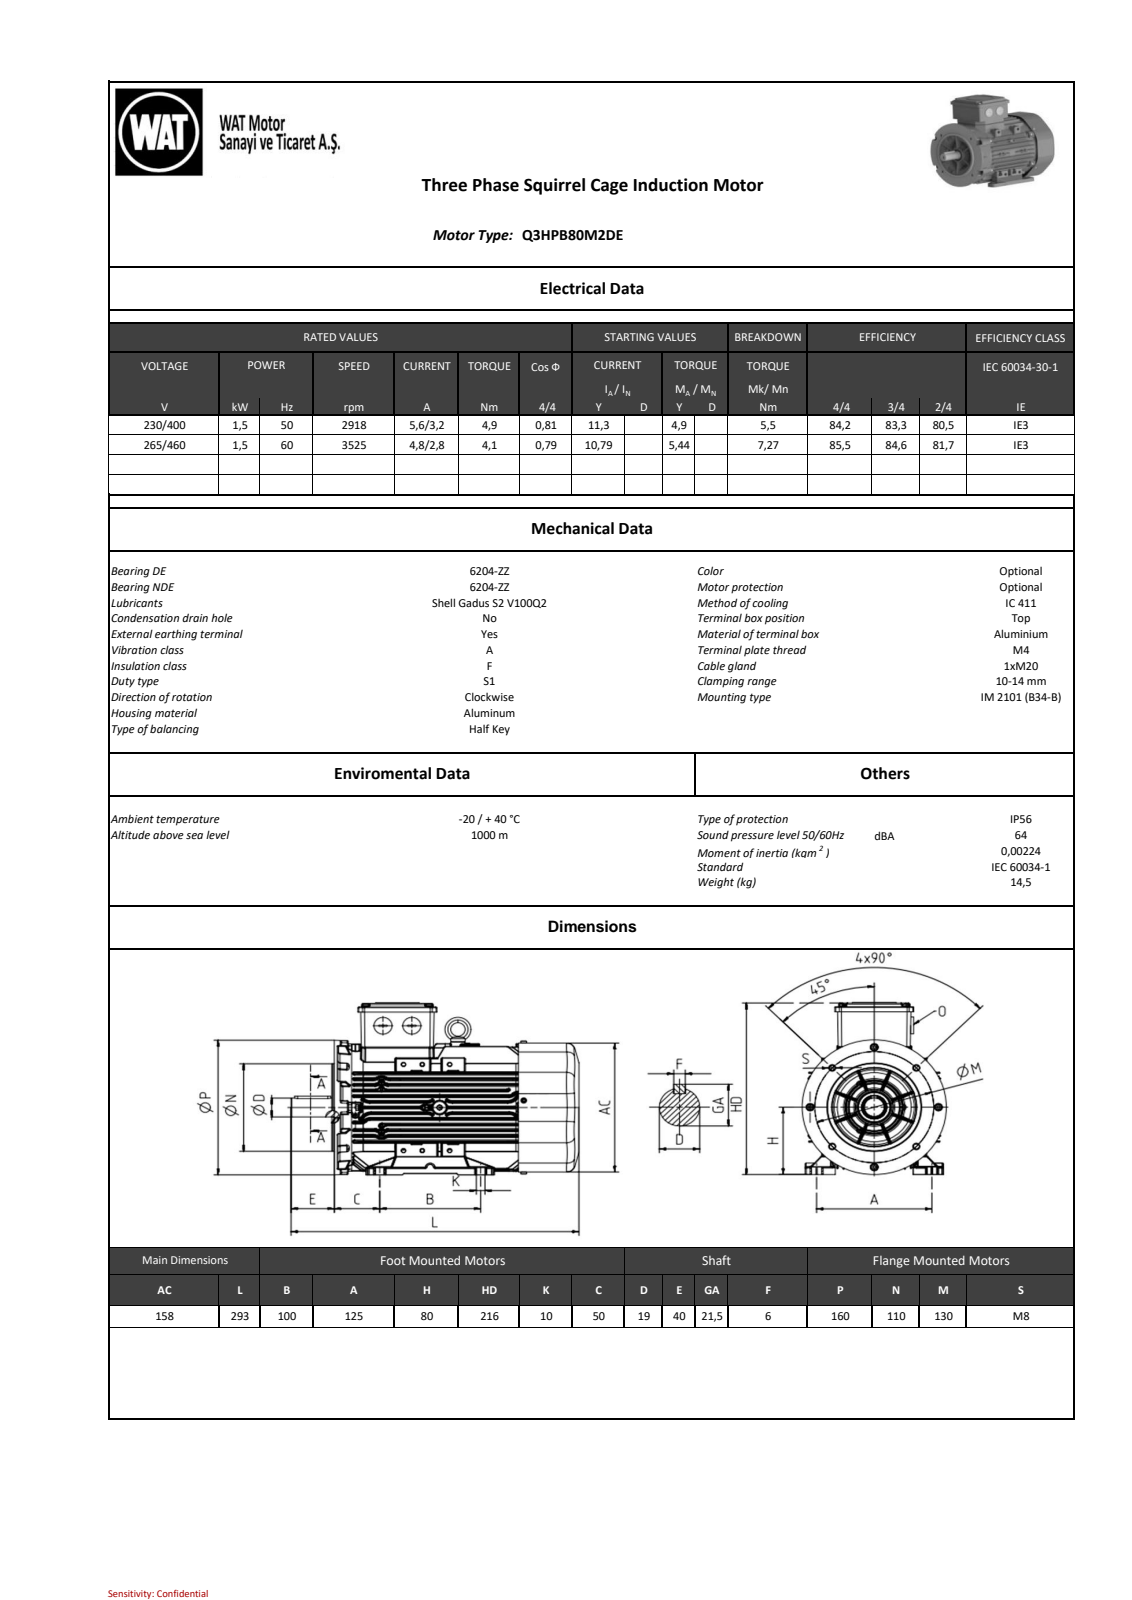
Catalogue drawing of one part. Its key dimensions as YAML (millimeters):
part_name: "model1"
step_written_by: "SIEMENS PLM Software NX2206.8101 (AUTOMOTIVE_DESIGN)"
units: millimeters
bodies: {solids: 0, faces: 6097, planar: 1209, cylindrical: 1771, other: 3117}
overall_size: [293, 215.5, 160]
round_holes:
  - {diameter: 3, count: 2}
  - {diameter: 3.5, count: 2}
  - {diameter: 4.6, count: 2}
  - {diameter: 5, count: 2}
  - {diameter: 3.3, count: 1}
  - {diameter: 8, count: 1}
  - {diameter: 57, count: 1}
round_bosses_or_shafts:
  - {diameter: 6, count: 5}
  - {diameter: 21.38, count: 2}
  - {diameter: 8.33, count: 2}
  - {diameter: 146.5, count: 1}
  - {diameter: 110, count: 1}
  - {diameter: 61, count: 1}
  - {diameter: 30, count: 1}
  - {diameter: 24.07, count: 1}
partial_cylinders:
  - {radius: 0.5, count: 567}
  - {radius: 1, count: 308}
  - {radius: 0.8, count: 281}
  - {radius: 2, count: 43}
  - {radius: 1.5, count: 18}
  - {radius: 5, count: 18}
  - {radius: 75.75, count: 8}
  - {radius: 2.25, count: 4}
face_to_face_distances: [1, 41.96, 10.36, 157, 156.98, 86, 18, 52.32, 221, 10.49]
hole_center_spacings: [25.5, 44.17, 50.3, 54.45, 70.94]
